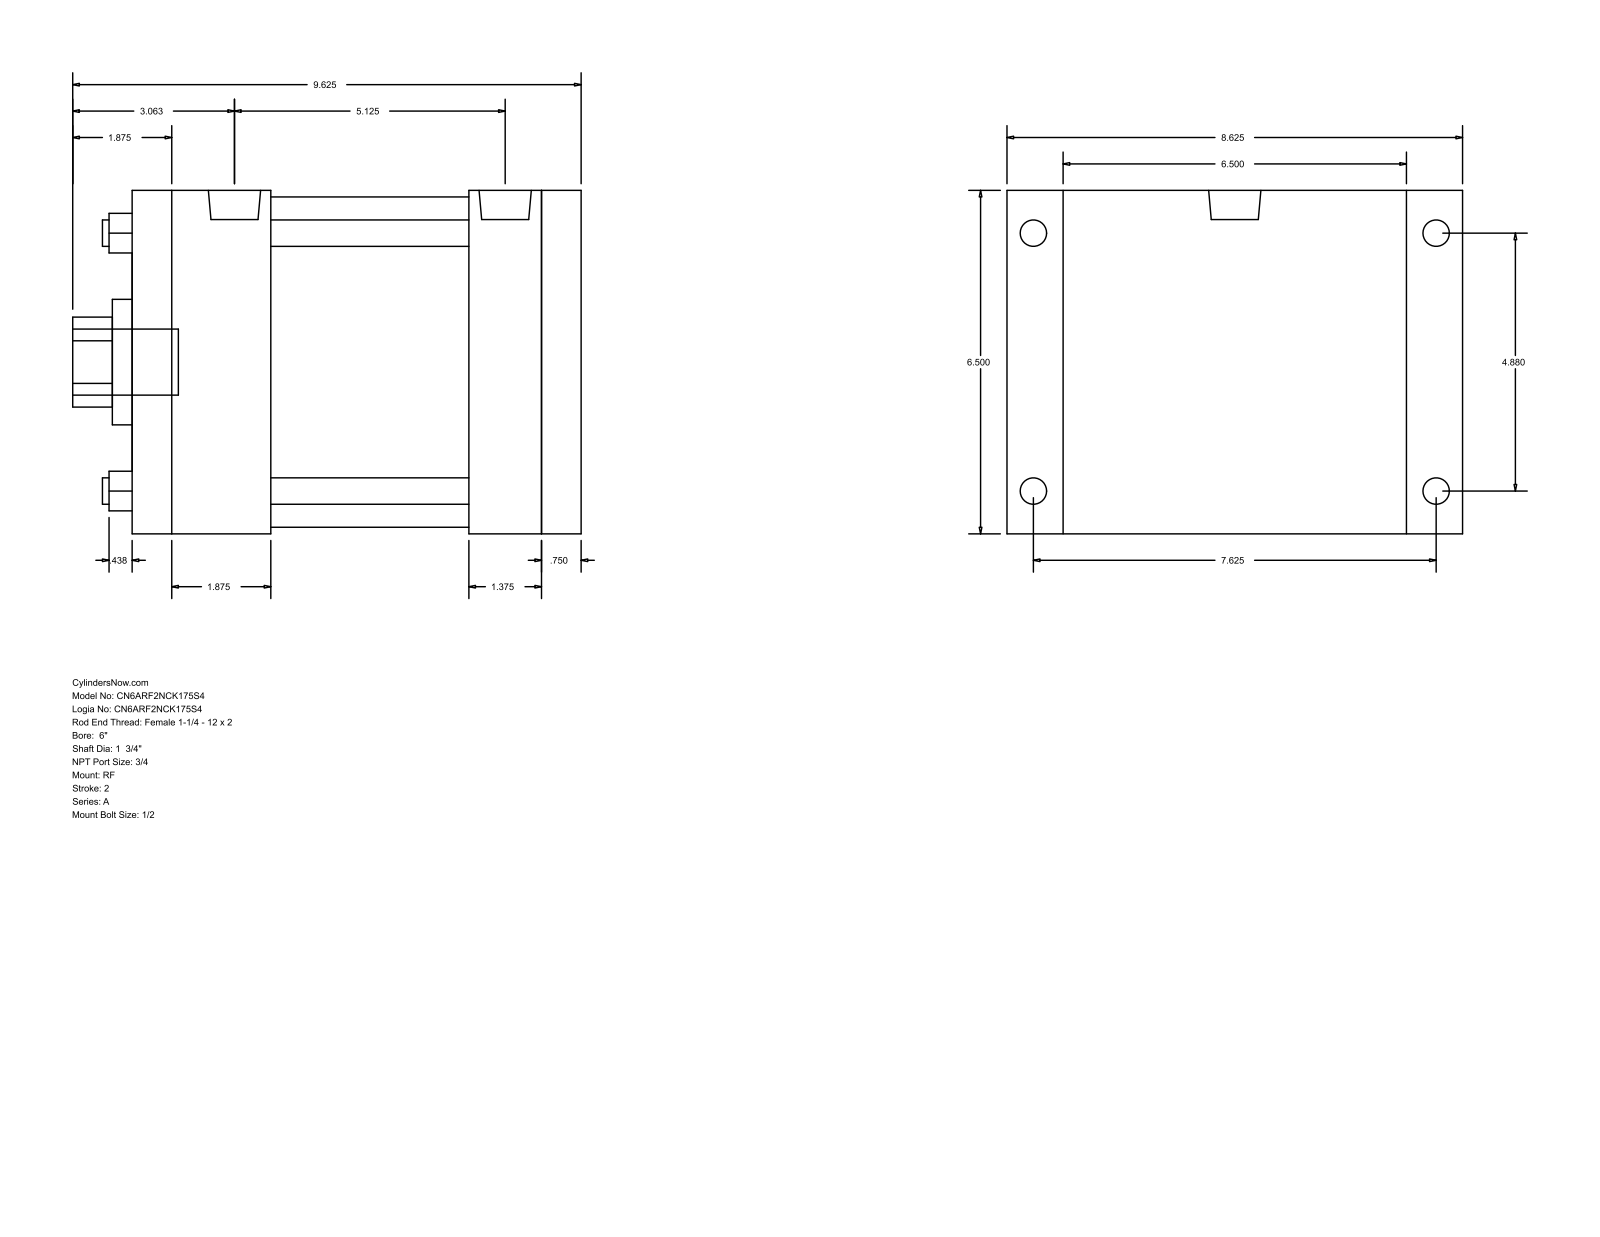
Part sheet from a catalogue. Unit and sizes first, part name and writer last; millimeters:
Units: millimetres
Overall size (bounding box): 244.47 × 219.07 × 165.1
Round holes (diameter × count): ⌀12.7 ×4, ⌀44.45 ×1, ⌀60.33 ×1, ⌀158.75 ×1
Round bosses / shafts (diameter × count): ⌀15.08 ×4, ⌀12.7 ×4, ⌀25.12 ×2, ⌀31.75 ×1
Partial cylindrical surfaces — rounded edges, fillets, slot ends (radius × count): R21.63 ×1
Main face-to-face distances: 165.1, 215.9, 196.86, 19.04, 95.25, 66.68, 130.18, 149.22, 161.93, 34.93
Hole centre spacings: 87.65, 123.96, 175.31
Bodies: 0 solids, 92 faces (64 planar, 28 cylindrical, 0 other)
Part name (STEP PRODUCT): A_RF__0600_1.75
STEP written by: GSSL Pune (CONFIG_CONTROL_DESIGN)
